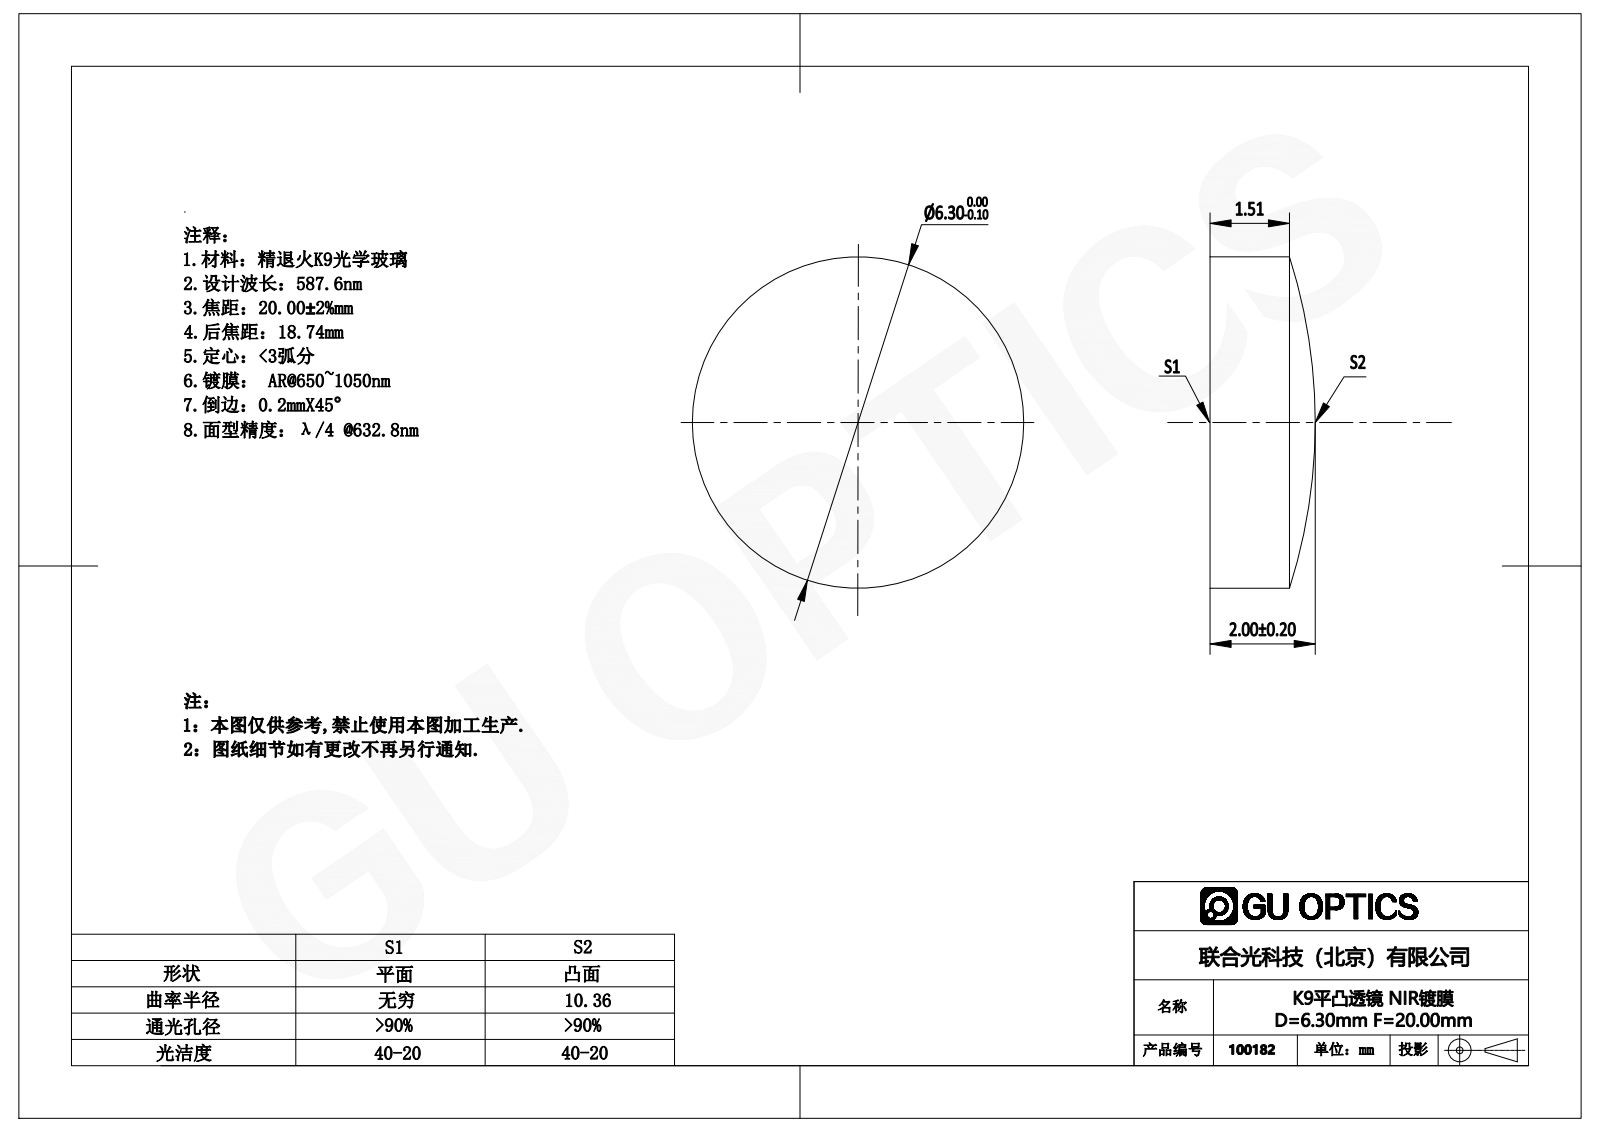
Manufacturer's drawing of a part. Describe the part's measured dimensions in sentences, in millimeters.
The part is named "100182". Its 3-D file was written by "SolidWorks 2016 (AUTOMOTIVE_DESIGN)". It is 1 solid with 5 faces: 1 planar, 2 cylindrical and 2 other. Overall it measures 6.3 by 6.3 by 2 millimeters. Its volume is 55 cubic millimeters and its surface area 93 square millimeters. Round bosses or shafts: 1 of diameter 6.3.
